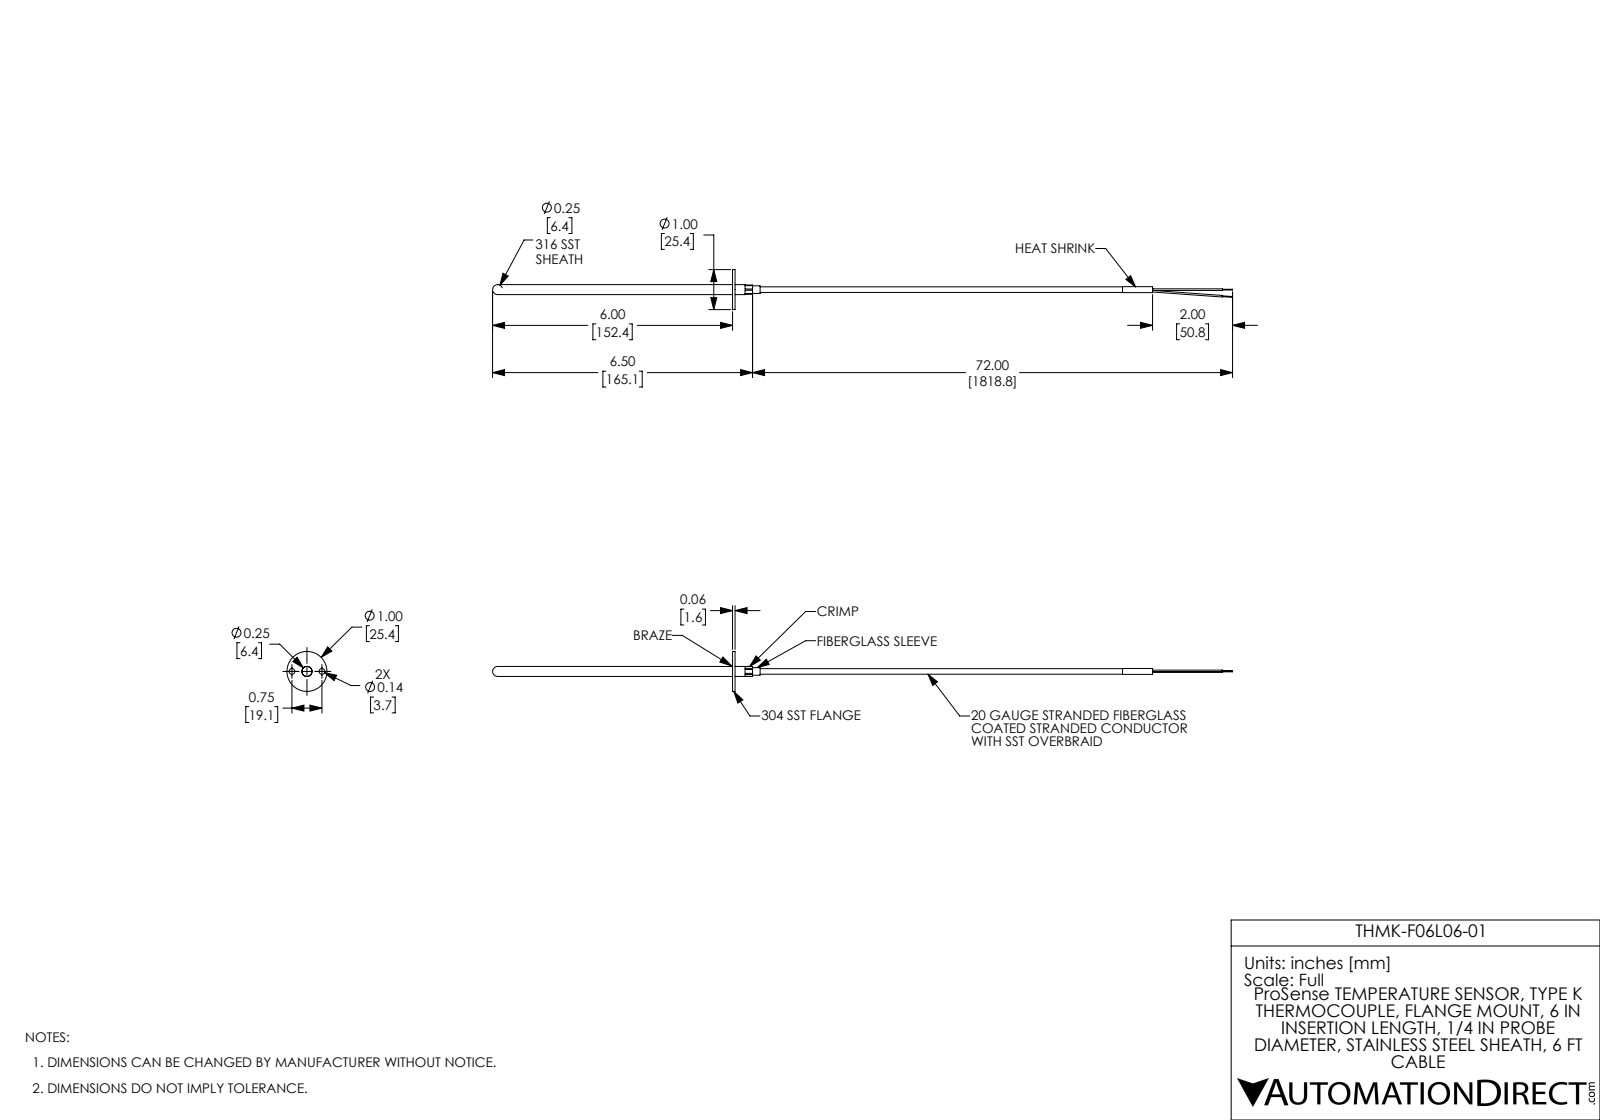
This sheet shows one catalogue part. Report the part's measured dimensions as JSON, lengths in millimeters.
{"part_name": "THMK-F06L06-01", "step_written_by": "SolidWorks 2017 (AUTOMOTIVE_DESIGN)", "units": "millimeters", "bodies": {"solids": 7, "faces": 65, "planar": 30, "cylindrical": 32, "other": 3}, "overall_size": [469.9, 25.4, 25.4], "volume_mm3": 8720, "surface_area_mm2": 14350, "round_holes": [[3.7, 3], [3.5, 1], [4.8, 1], [6.5, 1]], "round_bosses_or_shafts": [[25.4, 1], [6.4, 1], [4.8, 1], [4.8, 1], [3.8, 1], [3.6, 1], [3.4, 1], [1, 1]], "face_to_face_distances": [1.6, 12.7, 11.1, 5.9, 4.8, 19.1, 1.6, 3.1, 14.3, 17.5], "hole_center_spacings": [9.5, 9.5, 19.1]}
